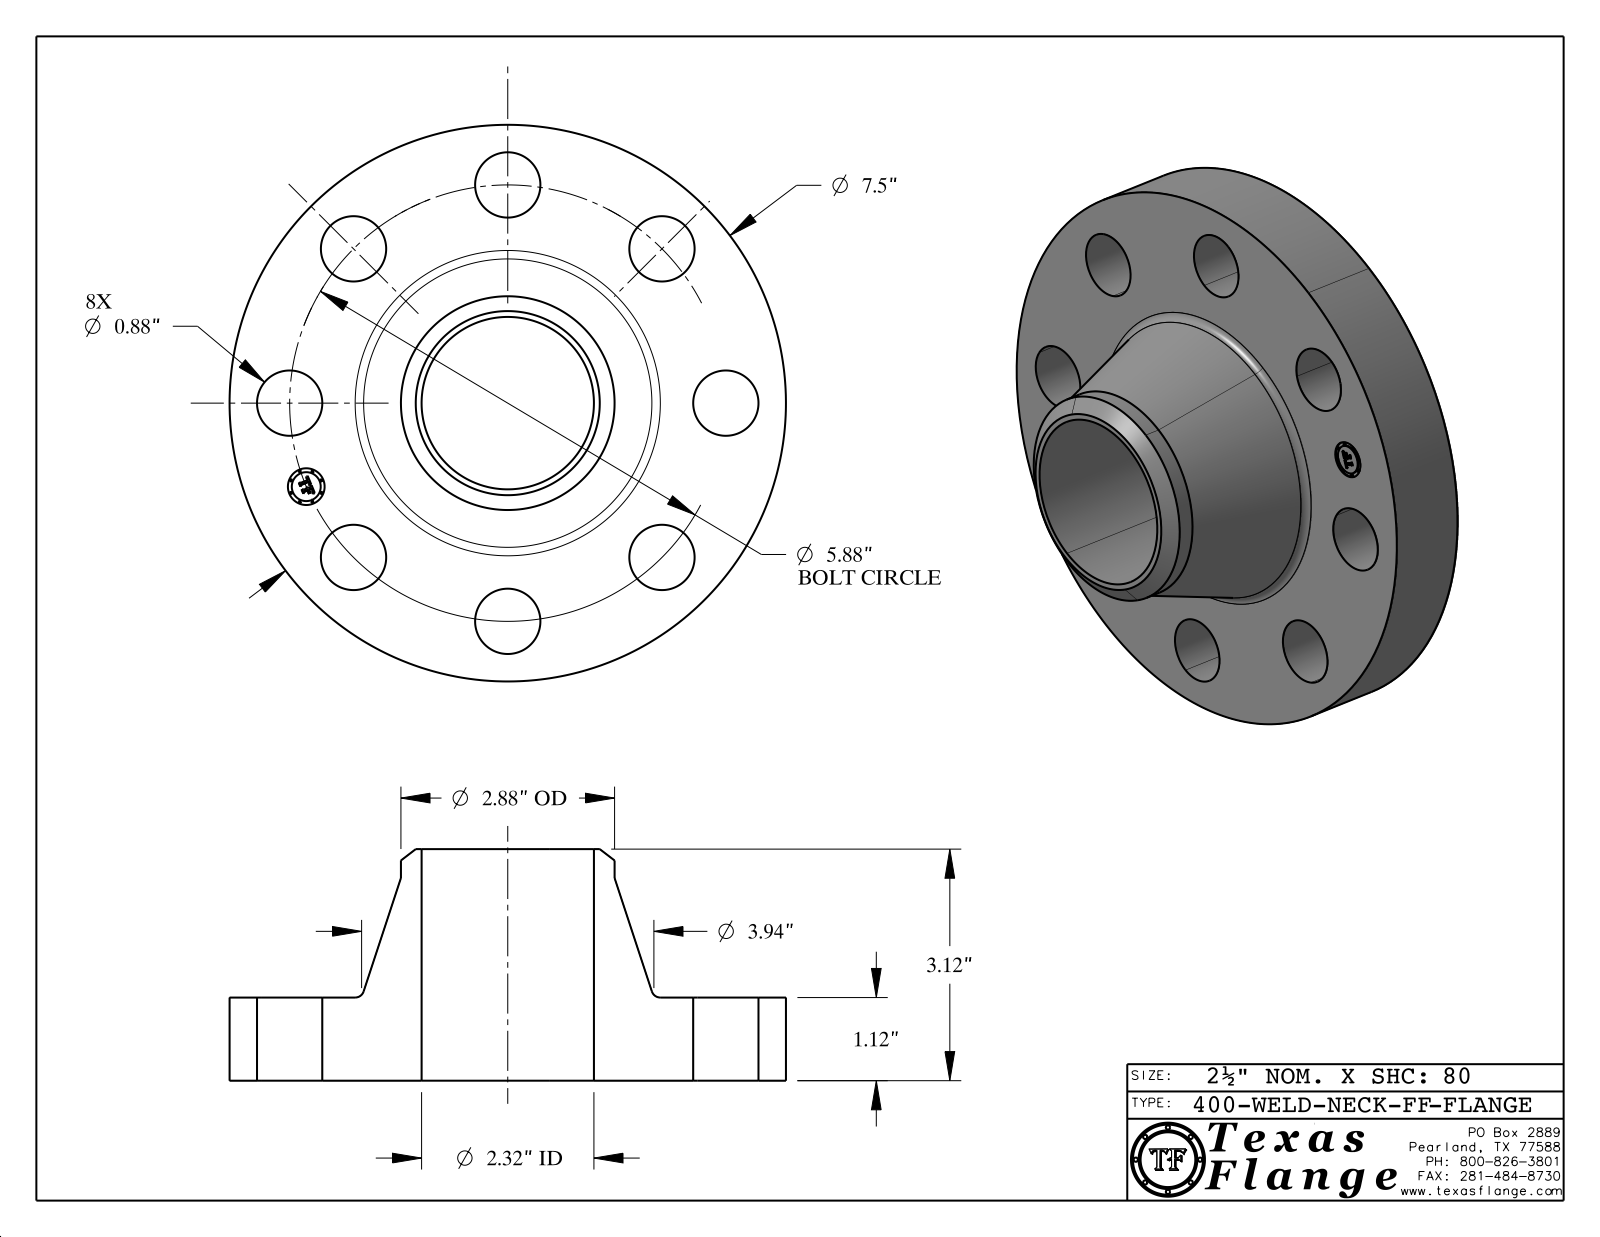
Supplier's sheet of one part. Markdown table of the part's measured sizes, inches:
| quantity | value |
| --- | --- |
| part name | 400-WELD-NECK-FF |
| STEP written by | CATIA V5 STEP AP214 (AUTOMOTIVE_DESIGN) |
| units | inches |
| bodies | 1 solid, 416 faces (368 planar, 42 cylindrical, 6 other) |
| overall size | 7.5 × 7.5 × 3.12 |
| volume | 48.06 in³ |
| surface area | 158.9 in² |
| round holes (diameter × count) | 0.88 × 8, 0.495 × 1, 2.323 × 1 |
| round bosses / shafts (diameter × count) | 0.03 × 8, 7.5 × 1, 2.88 × 1, 0.39 × 1 |
| main face-to-face distances | 1.12, 3.12, 2, 0.015, 1.105, 2.015, 0.148, 0.145, 0.027, 0.096 |
| hole center spacings | 2.25, 5.432, 2.94, 2.94, 4.157, 4.158, 3.267, 5.88 |
